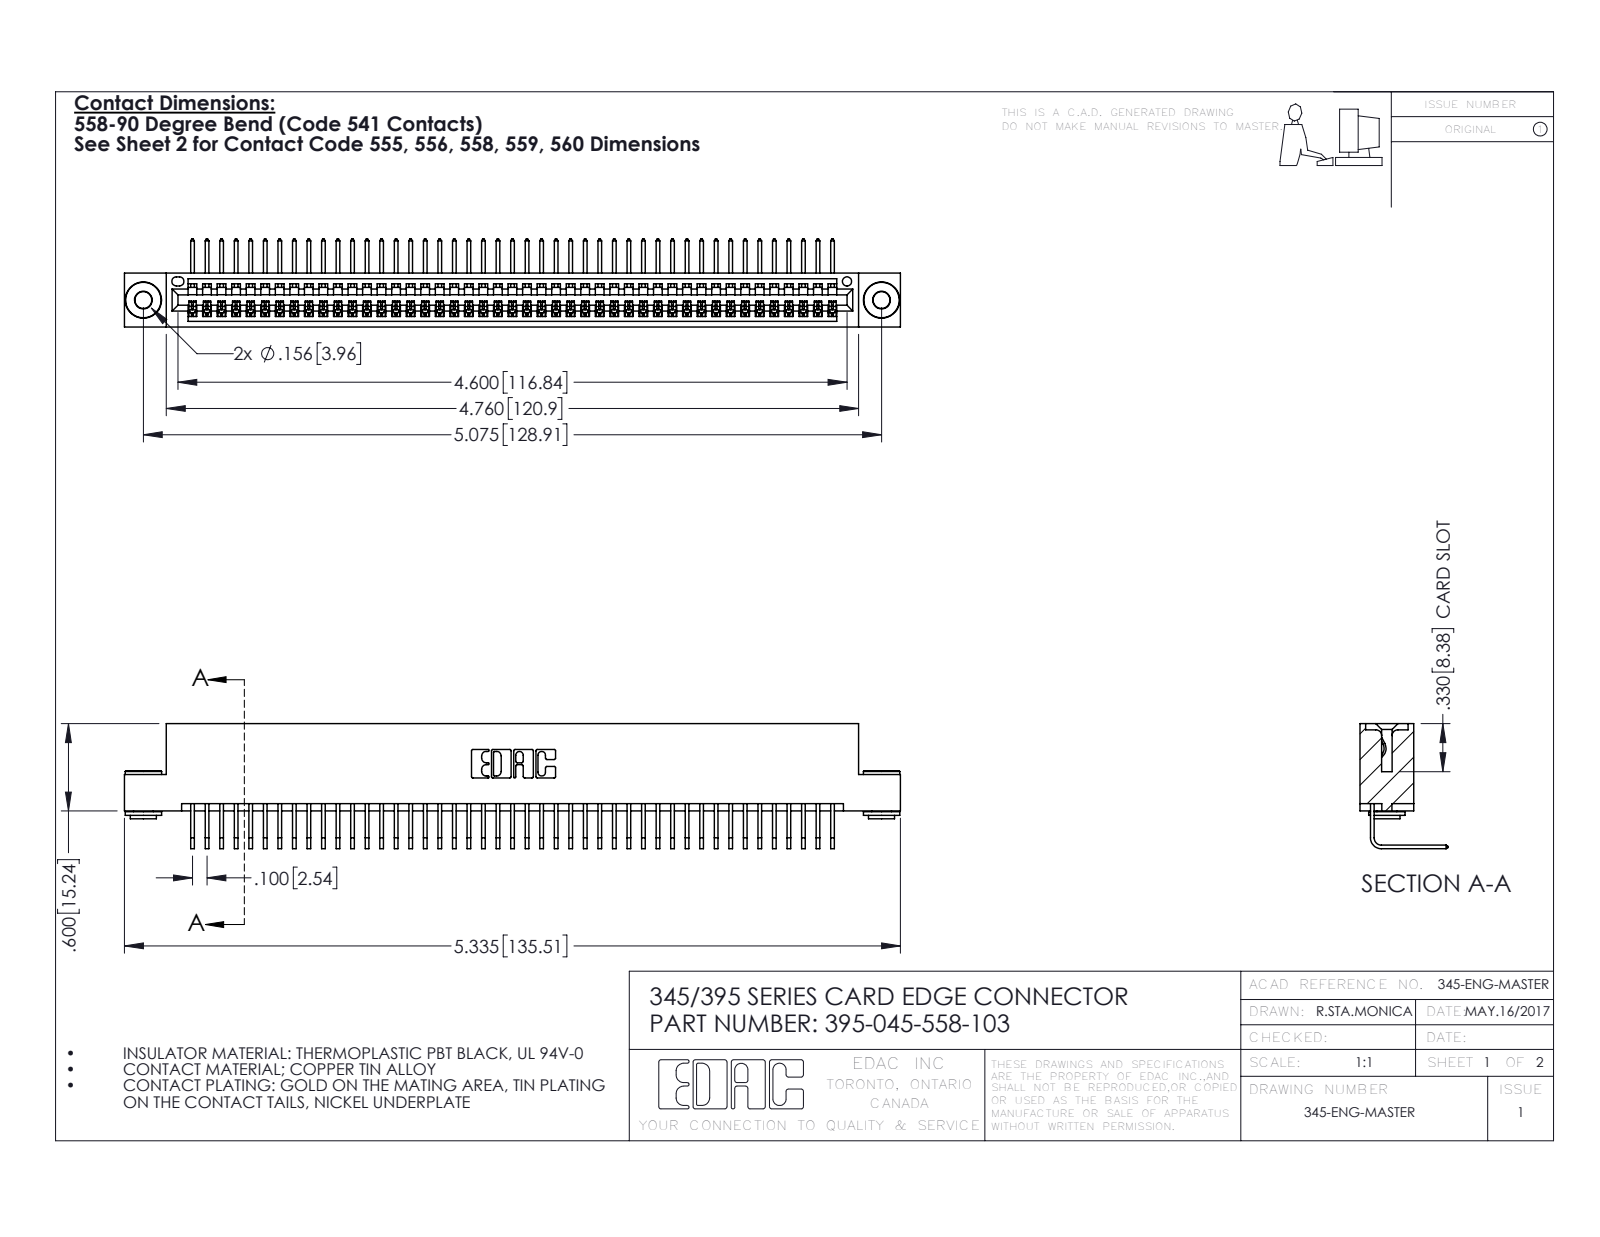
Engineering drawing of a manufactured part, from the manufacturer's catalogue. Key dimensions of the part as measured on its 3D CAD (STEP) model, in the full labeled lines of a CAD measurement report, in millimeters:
Part name (STEP PRODUCT): 345-292-001_558 Tail - 2; 345-250-002_345-250-002-102; 345 Part_Flush Mounting Lugs - 0.156 Dia-TH; 395-045-558-103
STEP written by: SolidWorks 2016 (CONFIG_CONTROL_DESIGN)
Units: millimetres
Bodies: 48 solids, 2864 faces (1980 planar, 876 cylindrical, 8 other)
Overall size (bounding box): 135.5 × 21.8 × 15.4
Volume: 13 100 mm³ · Surface area: 18 500 mm²
Round holes (diameter × count): ⌀2.9 ×2, ⌀4 ×2, ⌀1.6 ×1
Round bosses / shafts (diameter × count): ⌀6.4 ×2, ⌀4.6 ×2, ⌀3.5 ×2
Partial cylindrical surfaces — rounded edges, fillets, slot ends (radius × count): R0.2 ×90, R0.3 ×22, R0.2 ×6, R0.8 ×6, R0.7 ×3, R0.8 ×2, R1 ×2, R0.4 ×1
Main face-to-face distances: 1.8, 7.6, 9.4, 5.1, 0.6, 2.5, 6.9, 5.7, 3.8, 1.8
Hole centre spacings: 6.9, 122.9, 128.9
